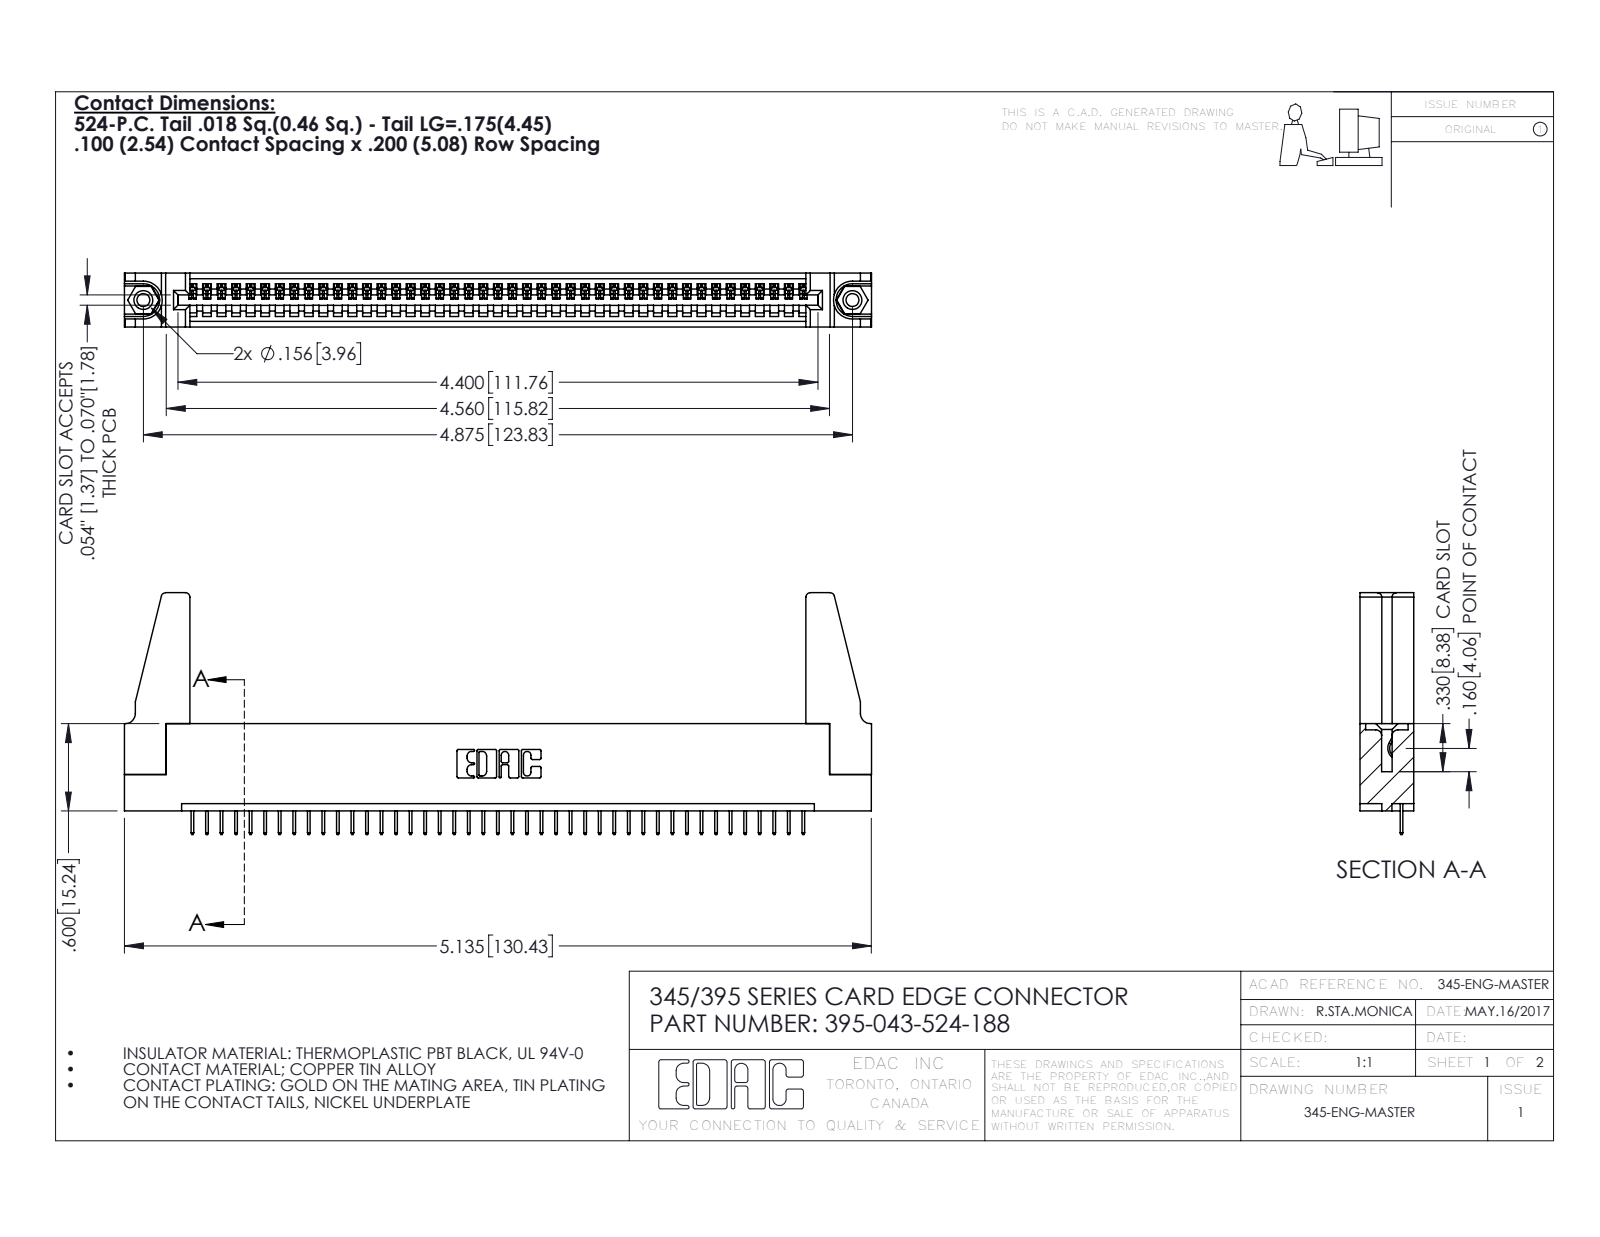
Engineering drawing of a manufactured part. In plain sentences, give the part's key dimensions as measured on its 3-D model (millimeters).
The part is named "345-250-001_345-250-001-102; 345-220-078_345-220-088; 345-292-001_345-293-124; 345 Part_Flush Mounting Lugs - 0.156 Dia-TH (+1 more)". Its 3-D file was written by "SolidWorks 2016 (CONFIG_CONTROL_DESIGN)". It is 48 solids with 2916 faces: 2130 planar, 770 cylindrical and 16 other. Overall it measures 130.5 by 42.2 by 9.4 millimeters. Its volume is 15 500 cubic millimeters and its surface area 18 850 square millimeters. Round holes: 2 of diameter 2.3, 2 of diameter 3.2, 2 of diameter 4, 1 of diameter 1.6. Round bosses or shafts: 2 of diameter 3.9. Partial cylindrical surfaces (rounded edges, fillets, slot ends): 86 of radius 0.2, 22 of radius 0.3, 8 of radius 0.8, 6 of radius 0.2, 6 of radius 0.8, 3 of radius 0.7, 2 of radius 0.8, 2 of radius 1. The main face-to-face distances are 1.8, 9.4, 7.6, 5.1, 2.5, 6.9, 0.6, 5.7, 1.8, 3.8. The hole center spacings are 6.9, 117.8, 123.8.
